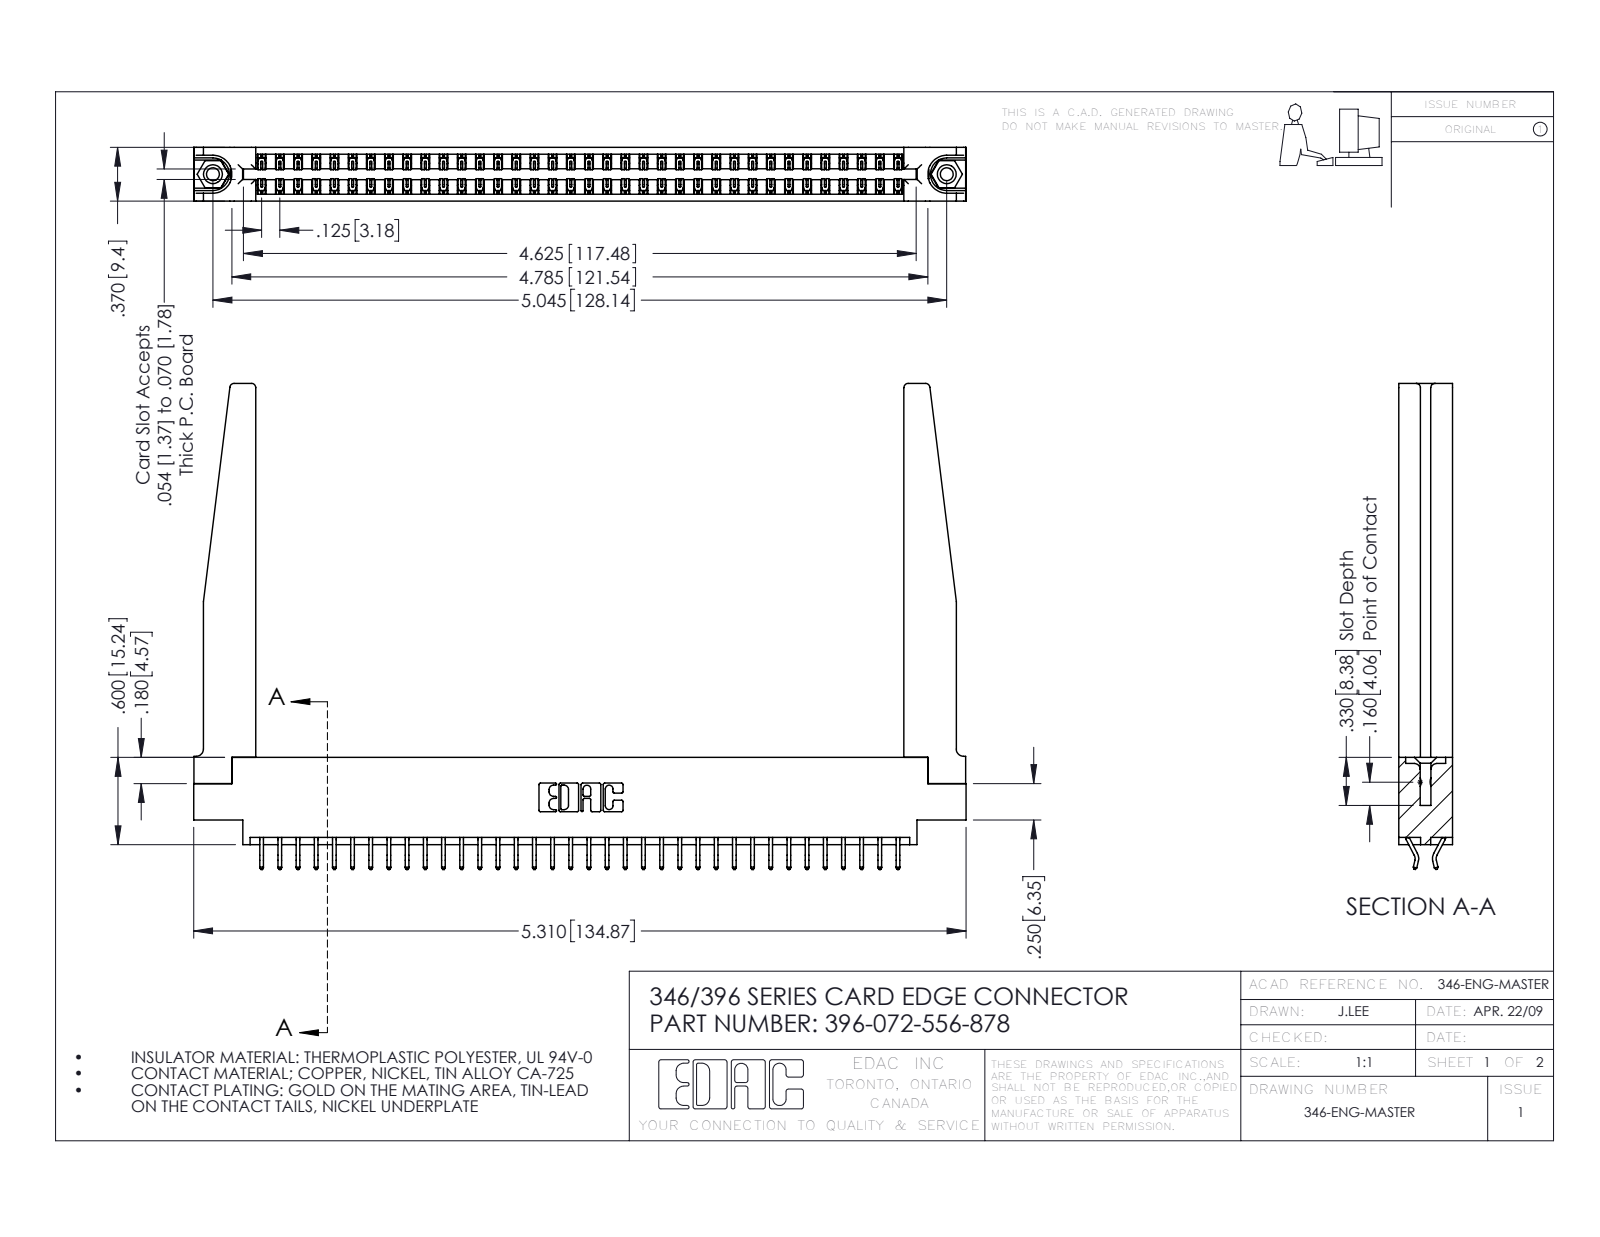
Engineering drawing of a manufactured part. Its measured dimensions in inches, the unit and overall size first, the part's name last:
Units: inches
Overall size (bounding box): 5.31 × 3.34 × 0.37
Round holes (diameter × count): ⌀0.089 ×2, ⌀0.125 ×2, ⌀0.156 ×2, ⌀0.064 ×1
Round bosses / shafts (diameter × count): ⌀0.155 ×2
Partial cylindrical surfaces — rounded edges, fillets, slot ends (radius × count): R0.006 ×108, R0.01 ×22, R0.03 ×8, R0.007 ×6, R0.031 ×6, R0.05 ×4, R0.026 ×3, R0.01 ×2
Main face-to-face distances: 0.37, 0.048, 0.322, 0.072, 0.148, 0.15, 0.25, 0.025, 0.298, 0.275
Hole centre spacings: 0.246, 4.836, 5.045
Volume: 1.212 in³ · Surface area: 37.75 in²
Bodies: 77 solids, 4536 faces (3030 planar, 1454 cylindrical, 52 other)
Part name (STEP PRODUCT): 346-220-078_345-220-078; 345-250-001_345-250-001-102; 346 Part_0.170 Offset - 0.156 Dia-TH; 345-292-001_556 Tail (+1 more)
STEP written by: SolidWorks 2016 (CONFIG_CONTROL_DESIGN)
